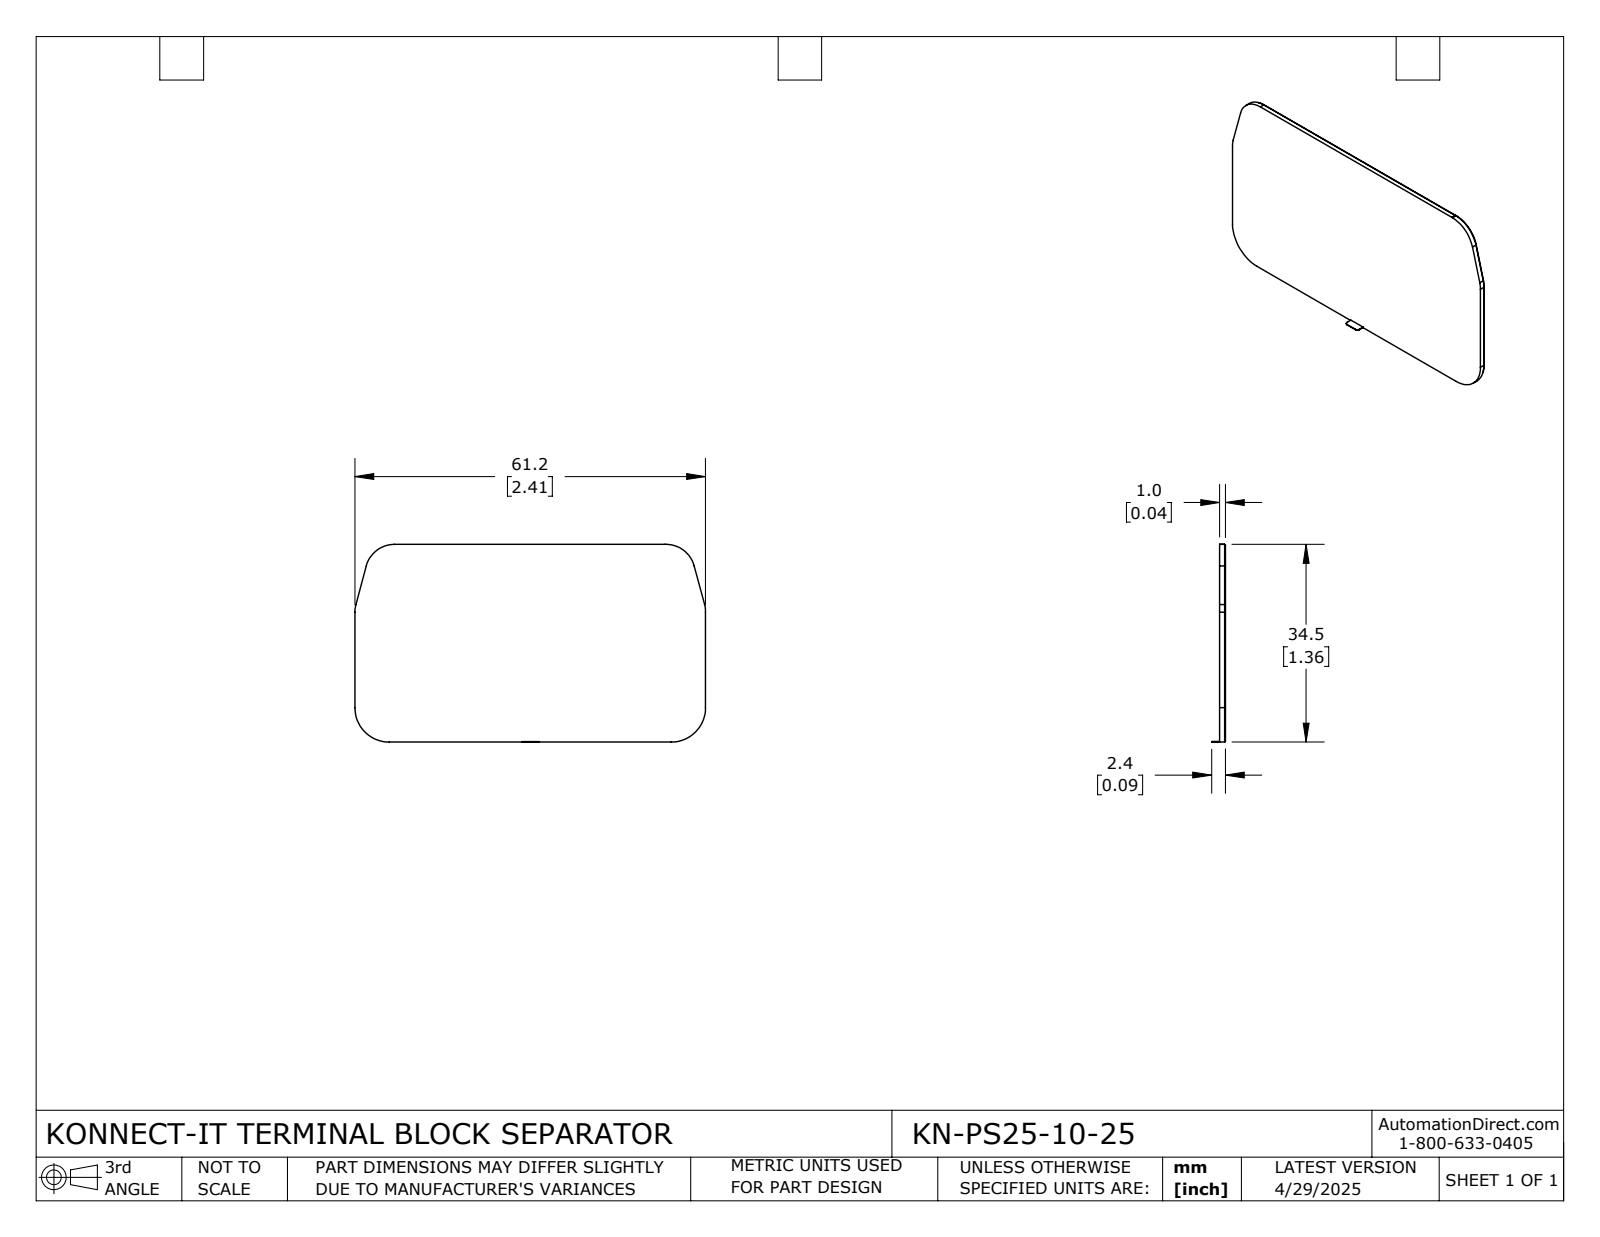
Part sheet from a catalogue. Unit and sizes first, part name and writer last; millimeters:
Units: millimetres
Overall size (bounding box): 61.23 × 34.51 × 2.4
Partial cylindrical surfaces — rounded edges, fillets, slot ends (radius × count): R5 ×4, R5.1 ×4, R0.5 ×2, R5.9 ×2, R6 ×2
Main face-to-face distances: 1, 34.51, 34.41, 0.85, 61.23, 34.31, 61.13, 61.03, 1.4, 2.25
Volume: 2 056 mm³ · Surface area: 4 304 mm²
Bodies: 1 solid, 35 faces (21 planar, 14 cylindrical, 0 other)
Part name (STEP PRODUCT): KN-PS25-10-25
STEP written by: SolidWorks 2024 (CONFIG_CONTROL_DESIGN)
